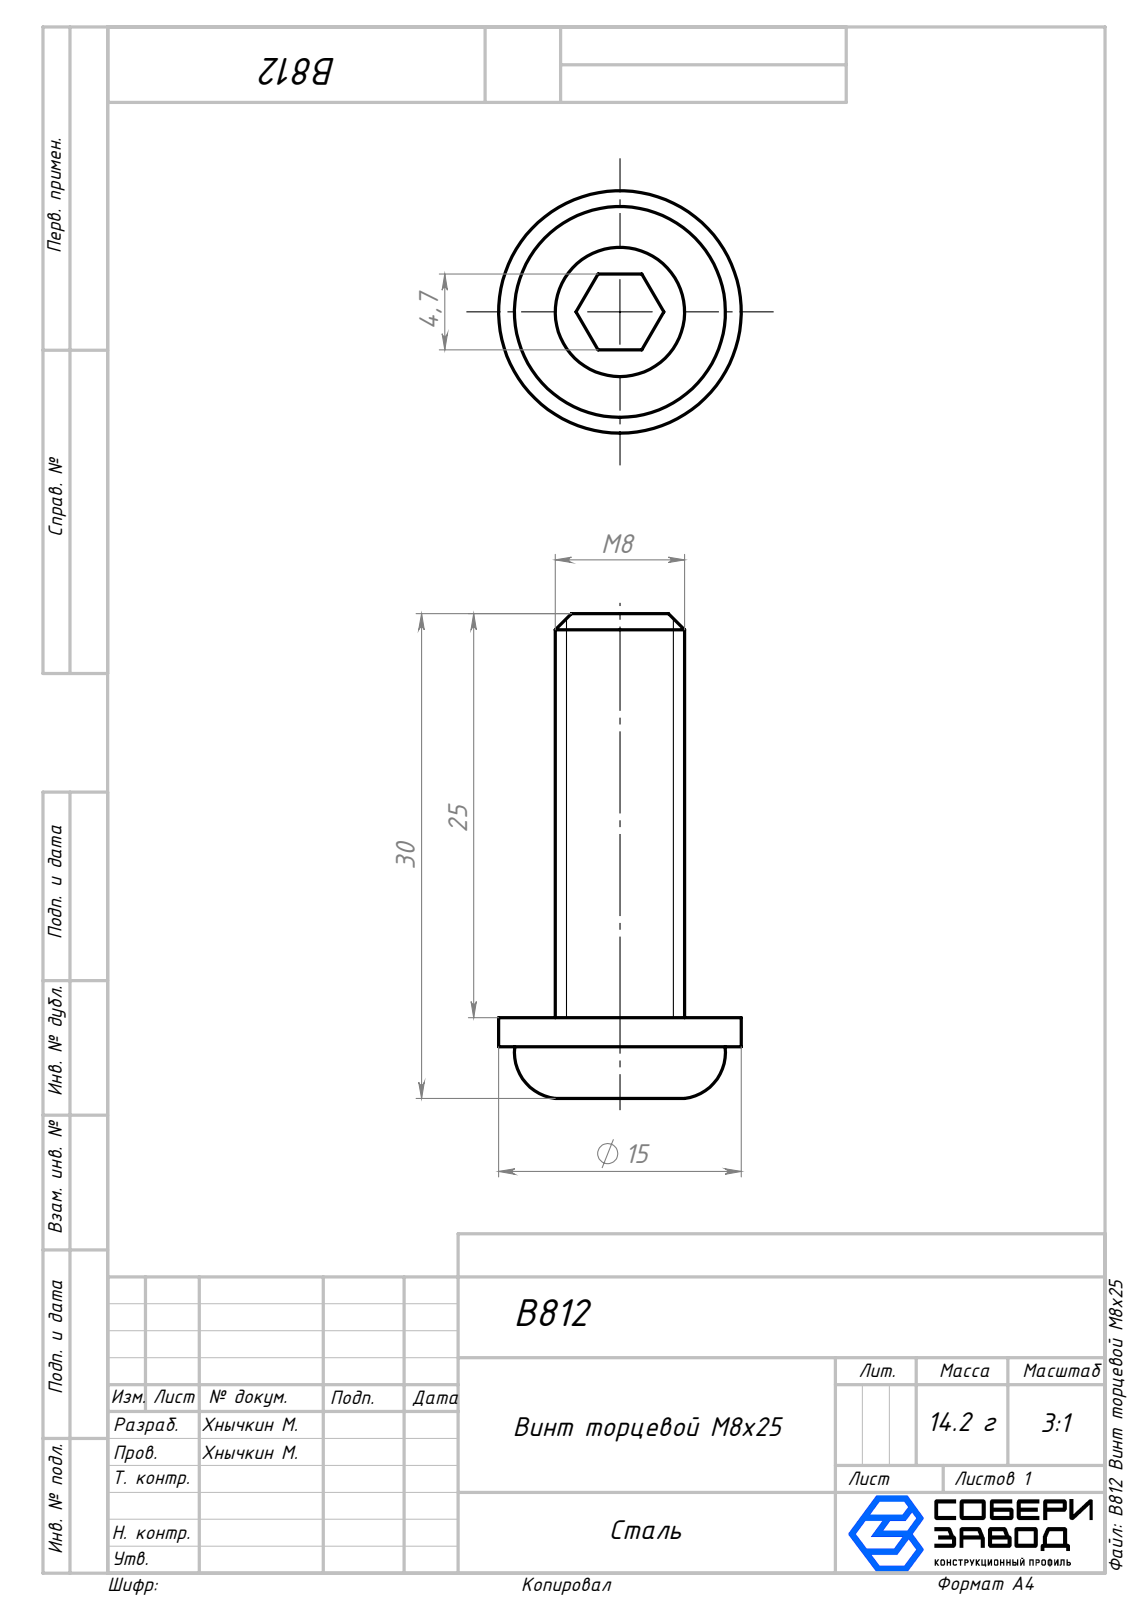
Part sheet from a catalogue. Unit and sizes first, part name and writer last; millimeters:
Units: millimetres
Overall size (bounding box): 30 × 15 × 15
Round bosses / shafts (diameter × count): ⌀15 ×1, ⌀8 ×1
Main face-to-face distances: 1.8, 4.7, 3.2, 5, 30, 26.8, 25, 4, 0.8, 1
Volume: 1 851 mm³ · Surface area: 1 194 mm²
Bodies: 1 solid, 19 faces (11 planar, 4 cylindrical, 4 other)
Part name (STEP PRODUCT): B812 Винт торцевой М8х25
STEP written by: SolidWorks 2026 (AUTOMOTIVE_DESIGN)
